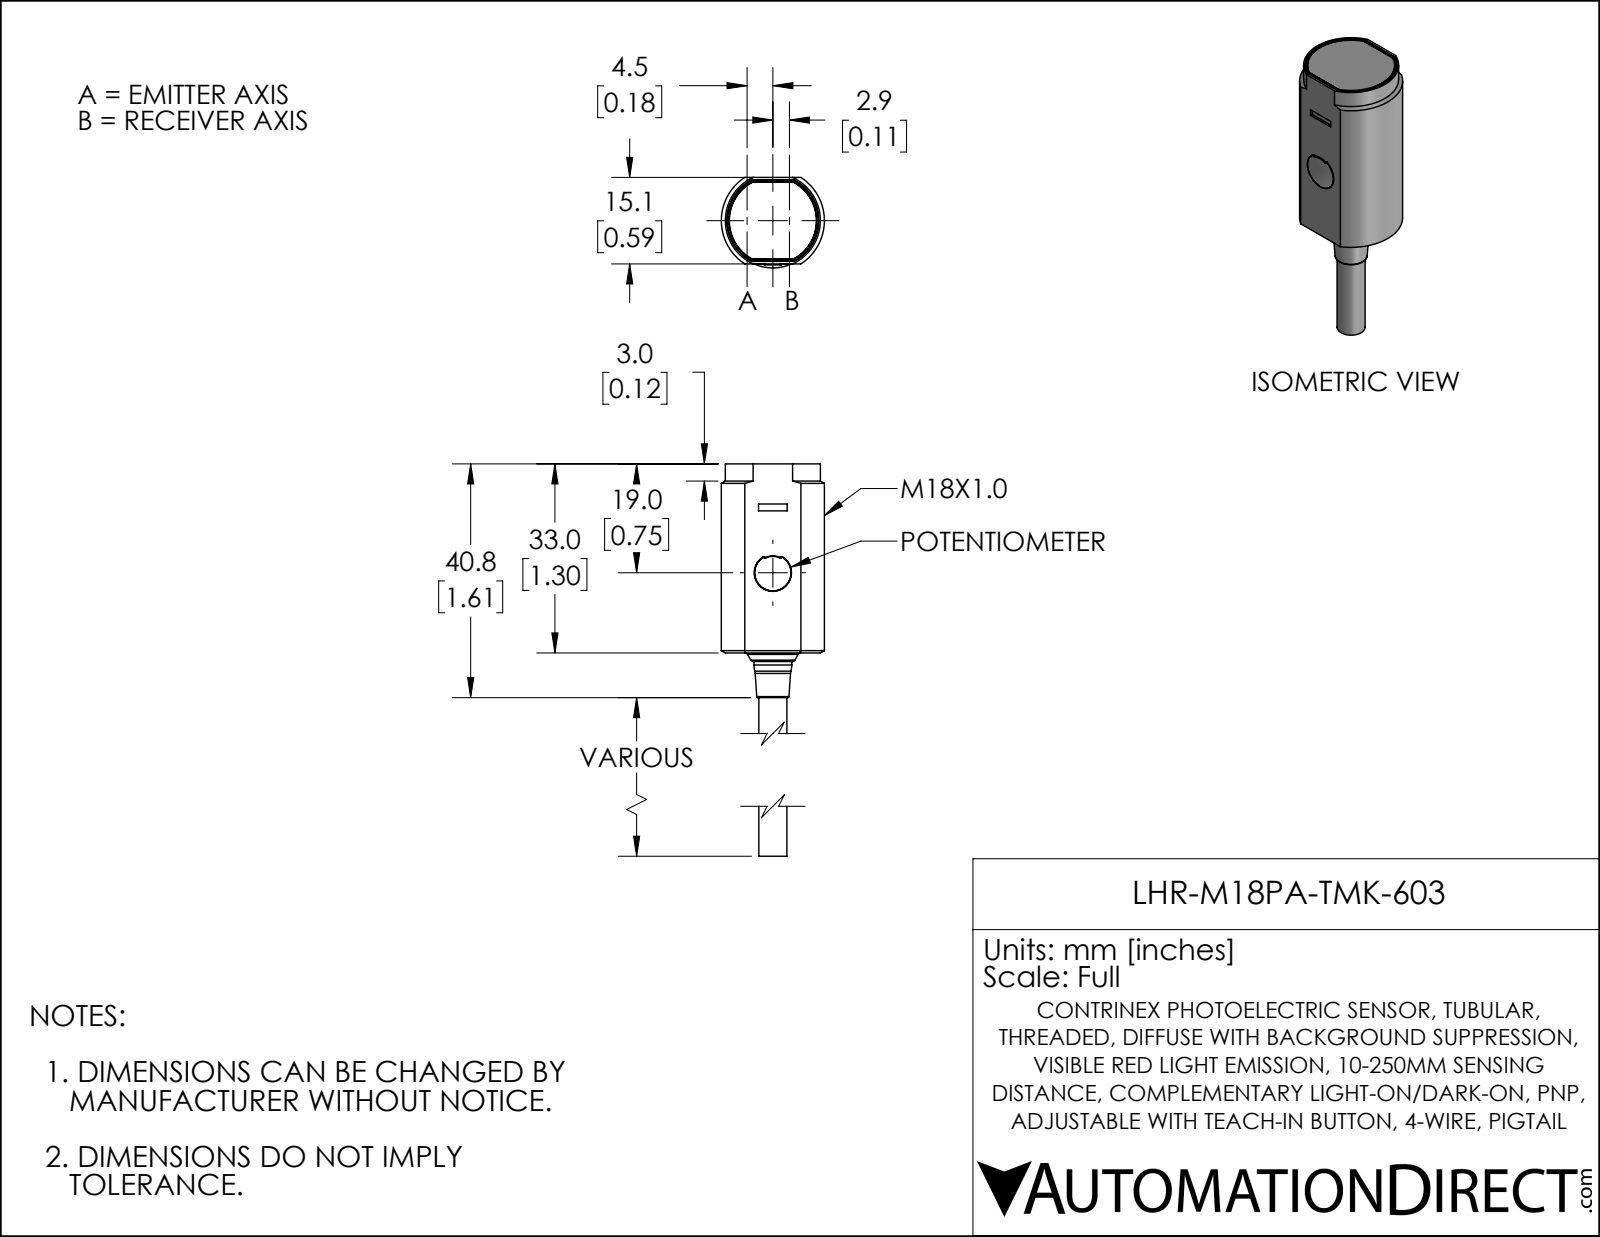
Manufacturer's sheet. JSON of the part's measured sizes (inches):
{"part_name": "LHR-M18PA-TMK-603", "step_written_by": "SolidWorks 2021 (AUTOMOTIVE_DESIGN)", "units": "inches", "bodies": {"solids": 1, "faces": 93, "planar": 39, "cylindrical": 41, "other": 13}, "overall_size": [2.205, 0.709, 0.622], "volume_in3": 0.501, "surface_area_in2": 4.23, "round_holes": [[0.256, 1]], "round_bosses_or_shafts": [[0.26, 1], [0.193, 1]], "partial_cylinders_radius": [[0.006, 8], [0.014, 8], [0.028, 8], [0.112, 1], [0.116, 1], [0.299, 1], [0.302, 1], [0.313, 1]], "face_to_face_distances": [0.594, 1.297, 1.299, 0.016, 2.205, 2.203, 0.906, 0.579, 0.014, 0.563]}
